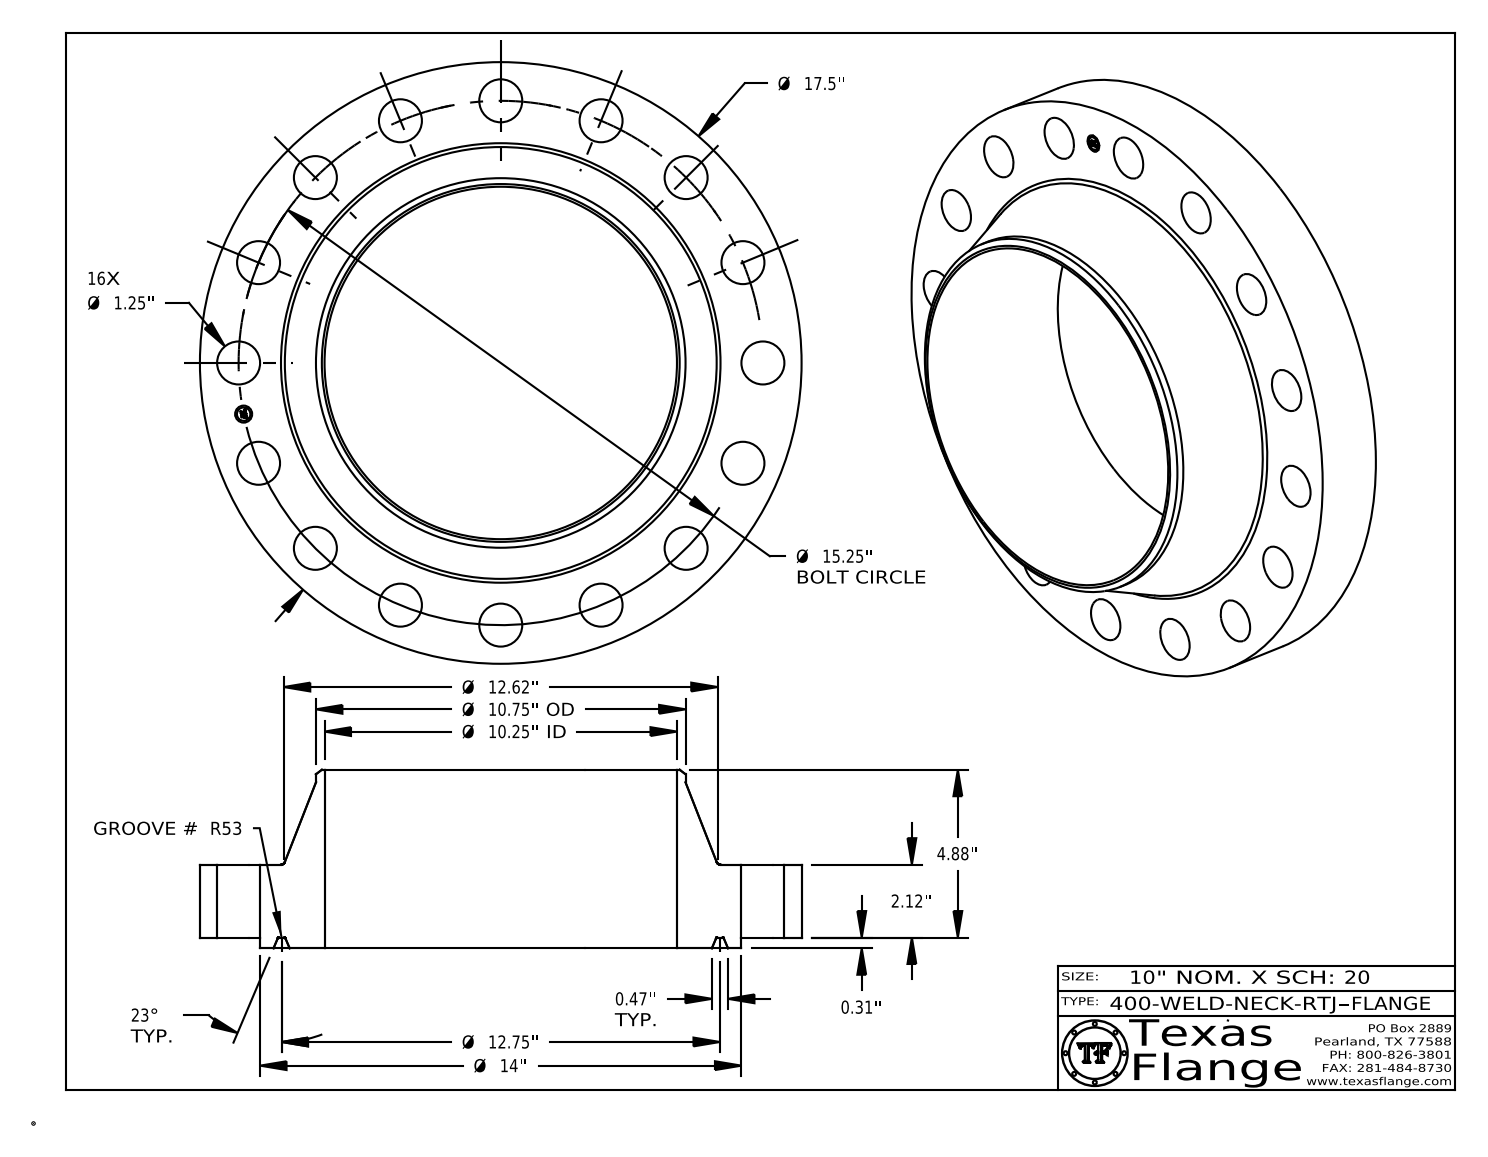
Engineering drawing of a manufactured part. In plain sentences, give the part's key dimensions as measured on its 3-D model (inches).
The part is named "400-WELD-NECK-RTJ". Its 3-D file was written by "CATIA V5 STEP AP214 (AUTOMOTIVE_DESIGN)". It is 1 solid with 445 faces: 371 planar, 60 cylindrical and 14 other. Overall it measures 17.5 by 17.5 by 5.193 inches. Its volume is 373.9 cubic inches and its surface area 792.4 square inches. Round holes: 16 of diameter 1.25, 1 of diameter 0.495, 1 of diameter 10.25. Round bosses or shafts: 8 of diameter 0.03, 1 of diameter 17.5, 1 of diameter 14, 1 of diameter 10.75, 1 of diameter 0.39. The main face-to-face distances are 2.12, 0.313, 2.433, 5.193, 4.88, 2.76, 0.015, 2.418, 2.105, 2.775. The hole center spacings are 8.472, 10.783, 14.957, 14.089, 7.625, 2.975, 2.975, 5.836.
